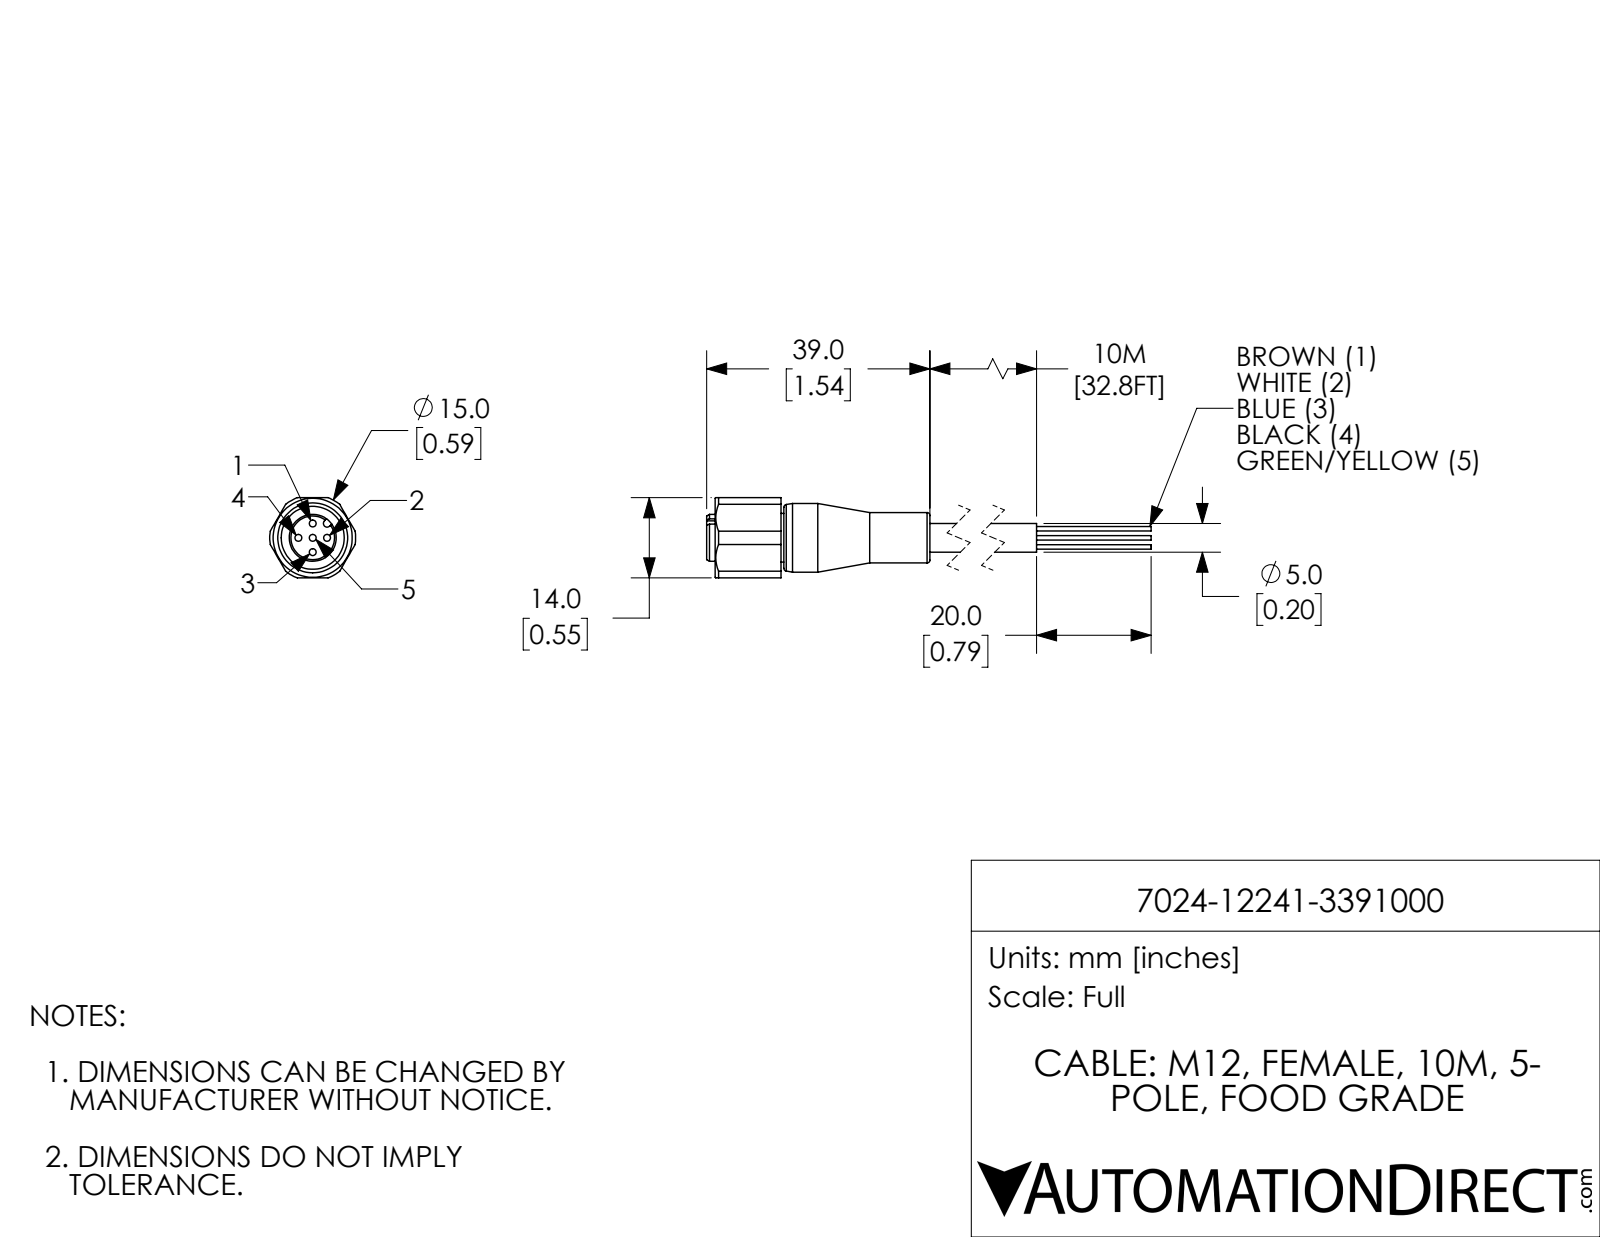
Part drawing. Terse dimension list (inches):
name: 7024-12241-3391000
written by: SolidWorks 2018 (AUTOMOTIVE_DESIGN)
unit: in
bodies: 1 solid, 80 faces (26 planar, 39 cylindrical, 15 other)
size: 3.063 × 0.591 × 0.551
volume: 0.252 in³; area: 4.458 in²
holes: 5× ⌀0.047, 1× ⌀0.433
bosses: 5× ⌀0.03, 1× ⌀0.472, 1× ⌀0.346, 1× ⌀0.335, 1× ⌀0.323, 1× ⌀0.197
rounds: 1× R0.026, 1× R0.295
face distances: 0.551, 0.157, 0.354, 0.512, 0.059, 0.295, 0.453, 0.531, 0.472, 0.177
hole spacings: 0.098, 0.139, 0.197
